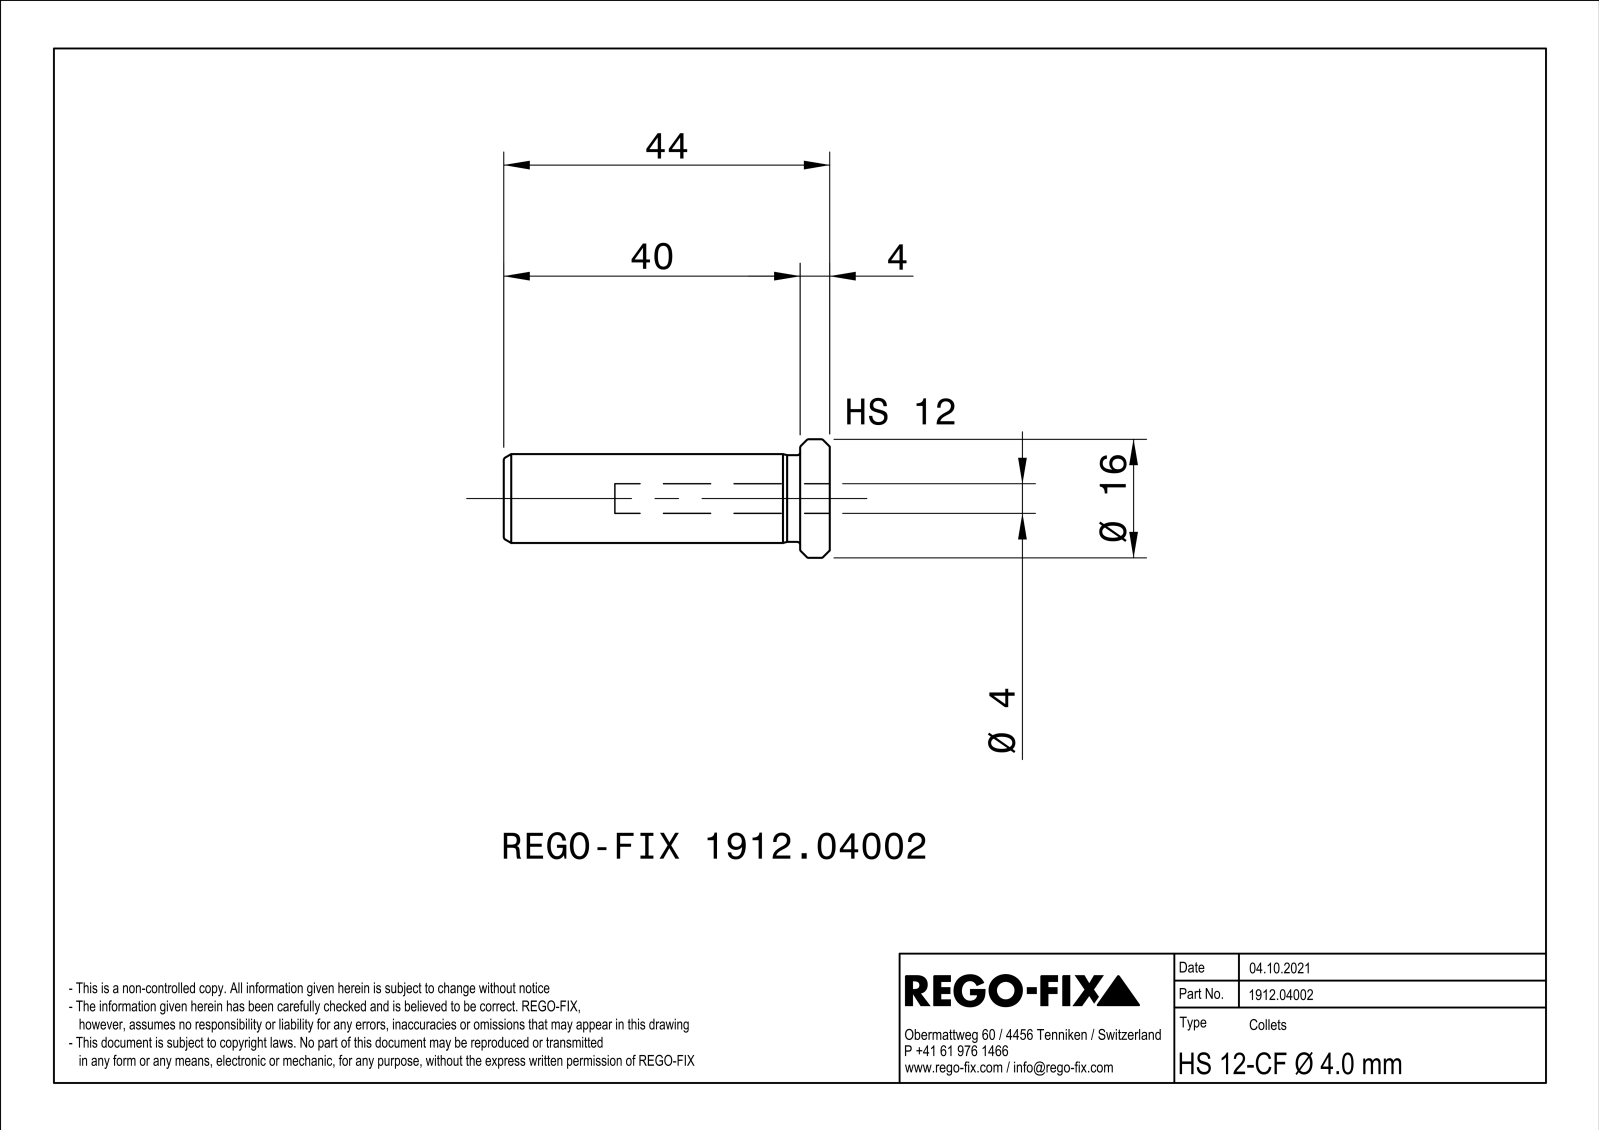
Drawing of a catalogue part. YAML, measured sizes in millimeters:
part_name: "NOCUT"
step_written_by: "SIEMENS PLM Software Solid Edge ST10 (AUTOMOTIVE_DESIGN)"
units: millimeters
bodies: {solids: 1, faces: 80, planar: 22, cylindrical: 18, other: 40}
overall_size: [44, 15.98, 15.98]
volume: 3877
surface_area: 3512
round_holes:
  - {diameter: 7.5, count: 1}
round_bosses_or_shafts:
  - {diameter: 16, count: 1}
  - {diameter: 12, count: 1}
  - {diameter: 11.7, count: 1}
partial_cylinders:
  - {radius: 0.4, count: 4}
  - {radius: 2, count: 1}
face_to_face_distances: [0.8, 44, 4, 40, 14.14]
